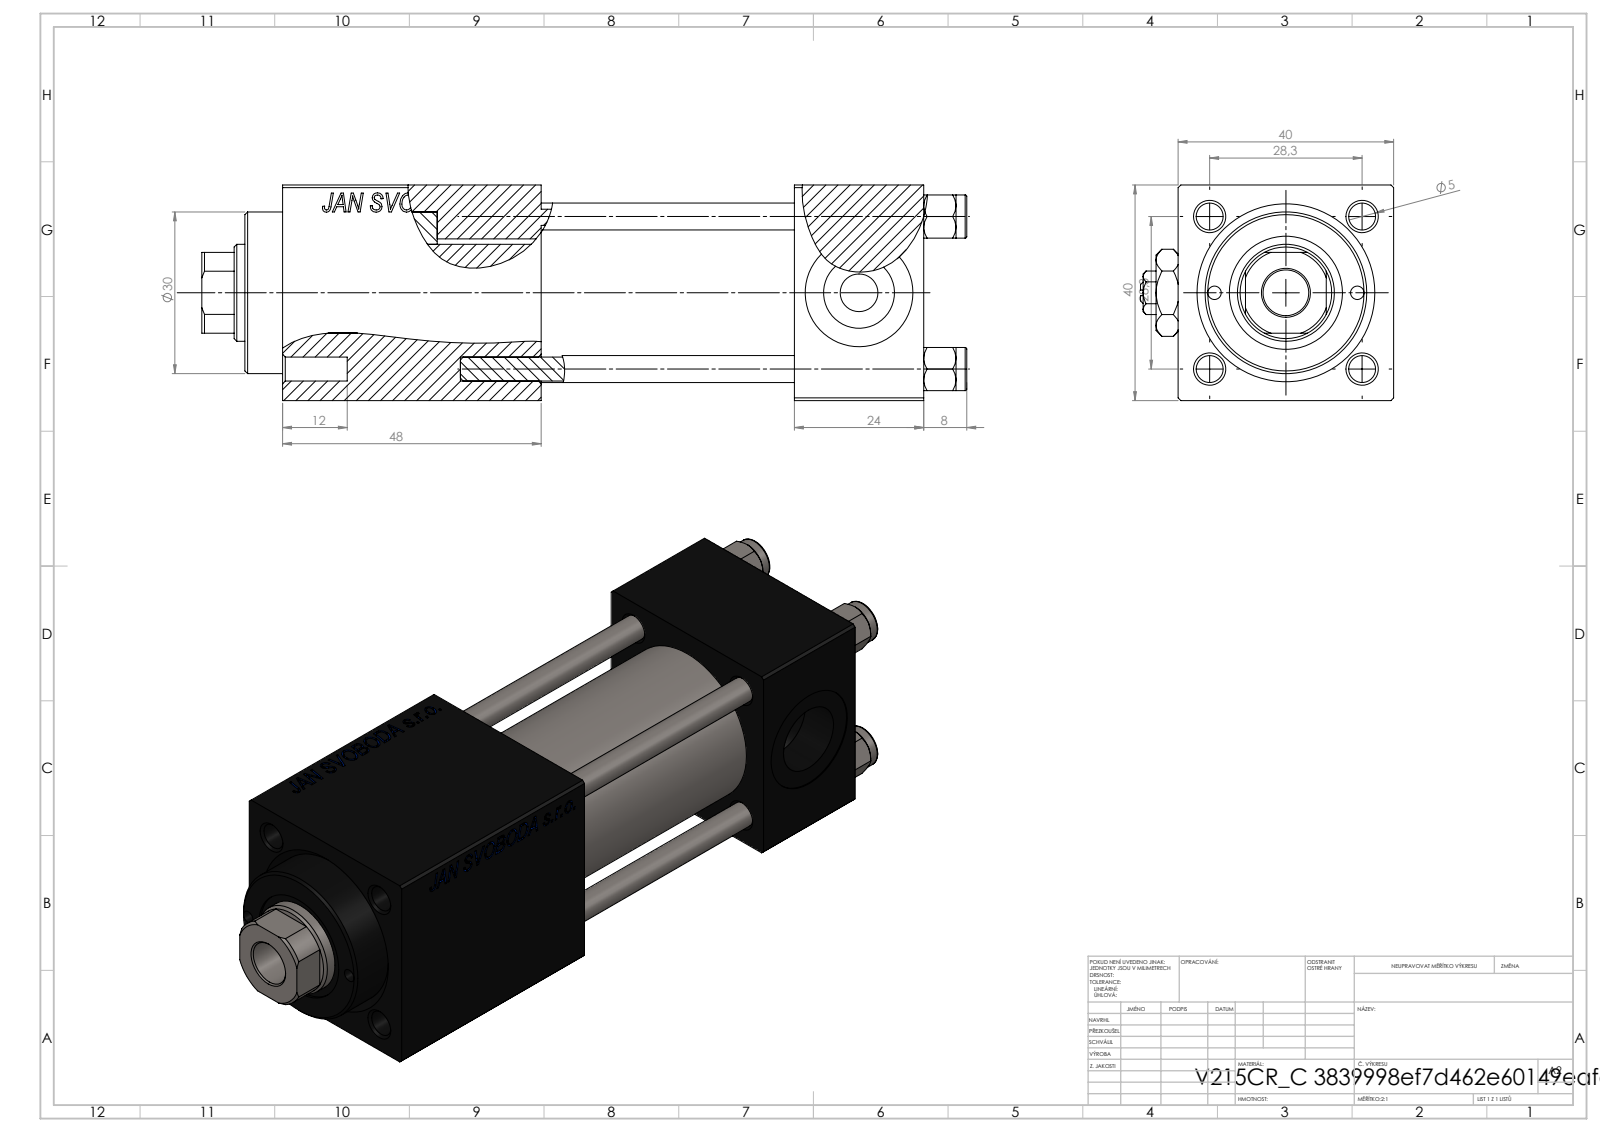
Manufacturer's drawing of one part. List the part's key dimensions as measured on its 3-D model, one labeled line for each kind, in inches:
Part name (STEP PRODUCT): NUT_M5_C; V215CR_C_Body; V215CR_C_TYCINKA; V215CR_VCP_C (+2 more)
STEP written by: SolidWorks 2019 (CONFIG_CONTROL_DESIGN)
Units: inches
Bodies: 12 solids, 1203 faces (549 planar, 96 cylindrical, 558 other)
Overall size (bounding box): 5.591 × 1.85 × 1.575
Volume: 9.1 in³ · Surface area: 89.79 in²
Round holes (diameter × count): ⌀0.197 ×4, ⌀0.787 ×3, ⌀0.098 ×2, ⌀0.276 ×2, ⌀0.518 ×2, ⌀0.335 ×1, ⌀0.709 ×1, ⌀0.827 ×1, ⌀0.984 ×1, ⌀1.181 ×1
Round bosses / shafts (diameter × count): ⌀0.315 ×4, ⌀1.22 ×1
Partial cylindrical surfaces — rounded edges, fillets, slot ends (radius × count): R0.335 ×1
Main face-to-face distances: 1.575, 0.945, 1.85, 2.795, 3.555, 2.61, 0.76, 1.89, 1.567, 3.74
Hole centre spacings: 0.558, 0.788, 1.114, 1.214, 0.522, 1.576, 1.043, 2.835
